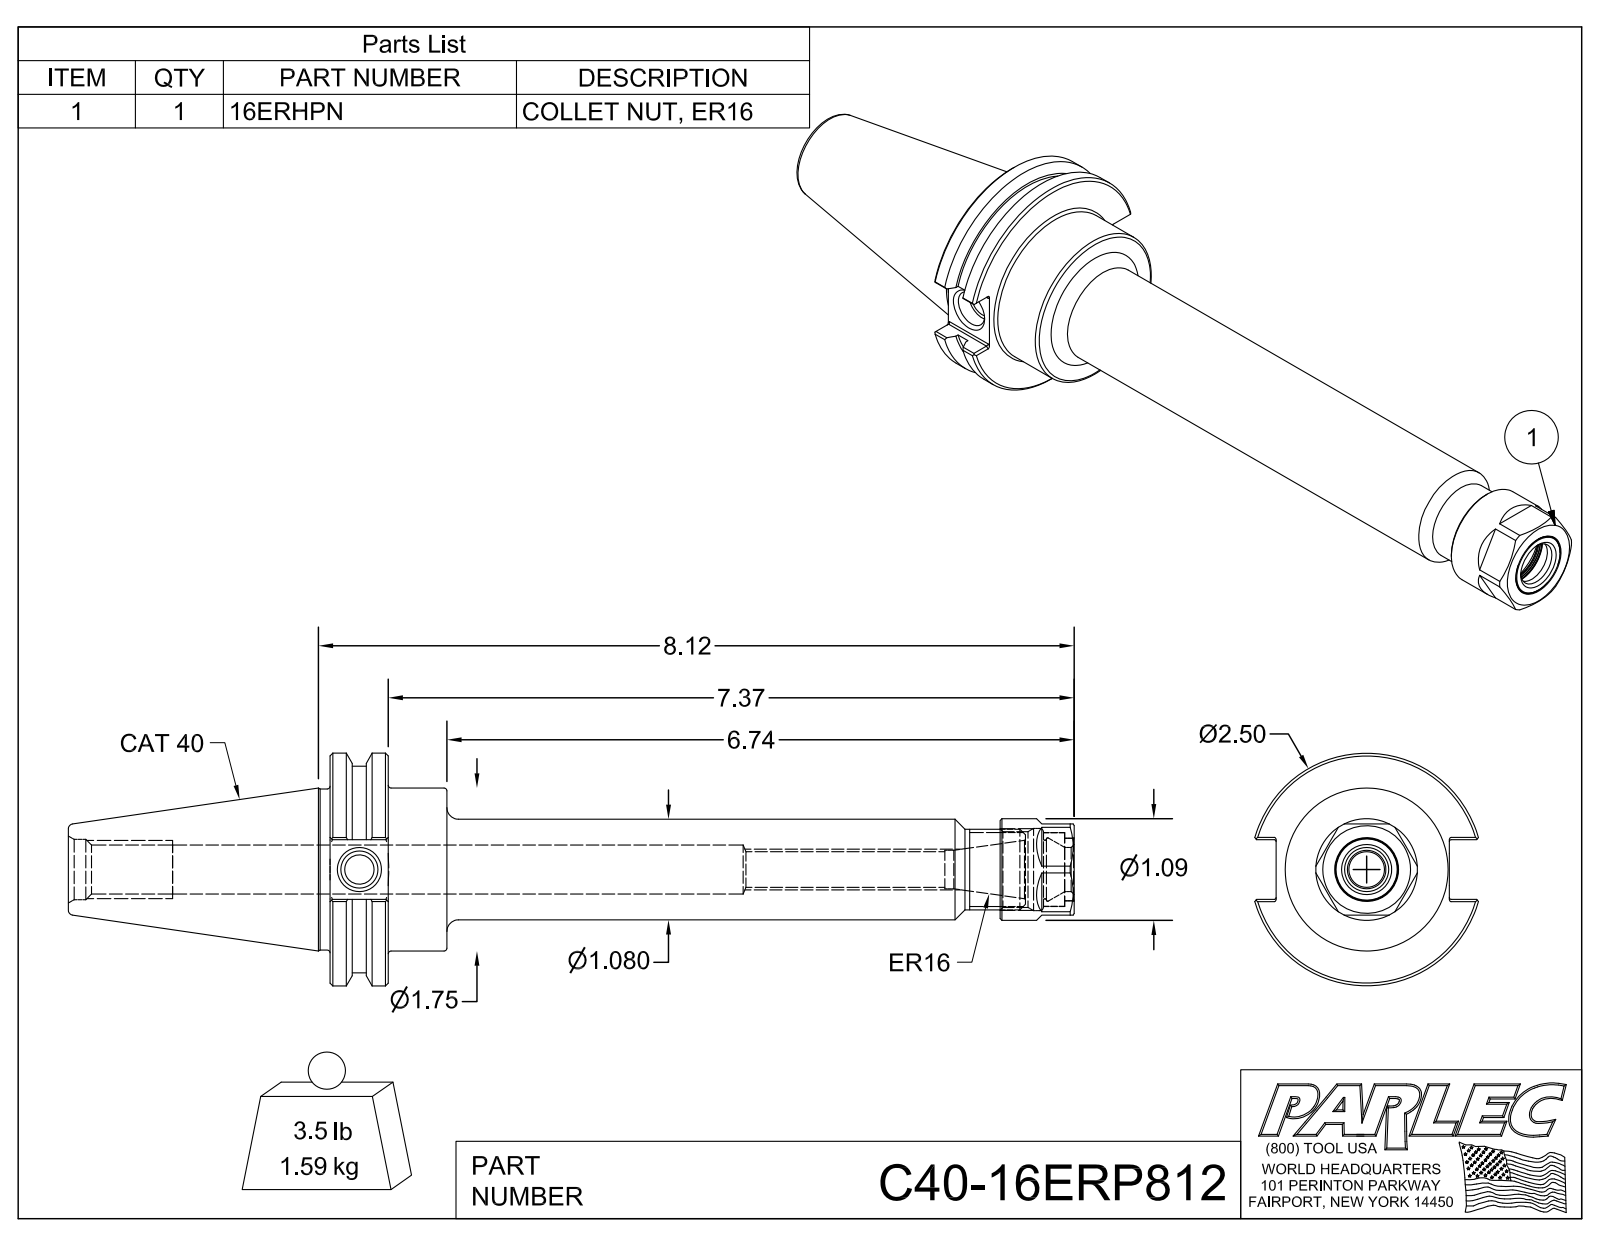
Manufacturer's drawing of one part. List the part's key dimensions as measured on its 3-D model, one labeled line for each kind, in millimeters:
Part name (STEP PRODUCT): C40-16ERP812; C40-16ER8-1; 16ERHPN
STEP written by: Autodesk Inventor 2018 (AUTOMOTIVE_DESIGN)
Units: millimetres
Bodies: 3 solids, 130 faces (53 planar, 39 cylindrical, 38 other)
Overall size (bounding box): 274.5 × 63.5 × 61
Volume: 200 100 mm³ · Surface area: 46 890 mm²
Round holes (diameter × count): ⌀8 ×1, ⌀9.7 ×1, ⌀10.1 ×1, ⌀10.5 ×1, ⌀12 ×1, ⌀13.4 ×1, ⌀13.4 ×1, ⌀16 ×1, ⌀16.5 ×1, ⌀17.1 ×1, ⌀17.3 ×1, ⌀20.2 ×1
Round bosses / shafts (diameter × count): ⌀63.5 ×1, ⌀56.4 ×1, ⌀44.5 ×1, ⌀43.9 ×1, ⌀27.7 ×1, ⌀27.4 ×1, ⌀22 ×1, ⌀20.1 ×1
Partial cylindrical surfaces — rounded edges, fillets, slot ends (radius × count): R0.5 ×12
Main face-to-face distances: 15.9, 31.9, 16, 24.9, 203.1, 187.2, 171.2, 4.3, 20.6, 182.9
